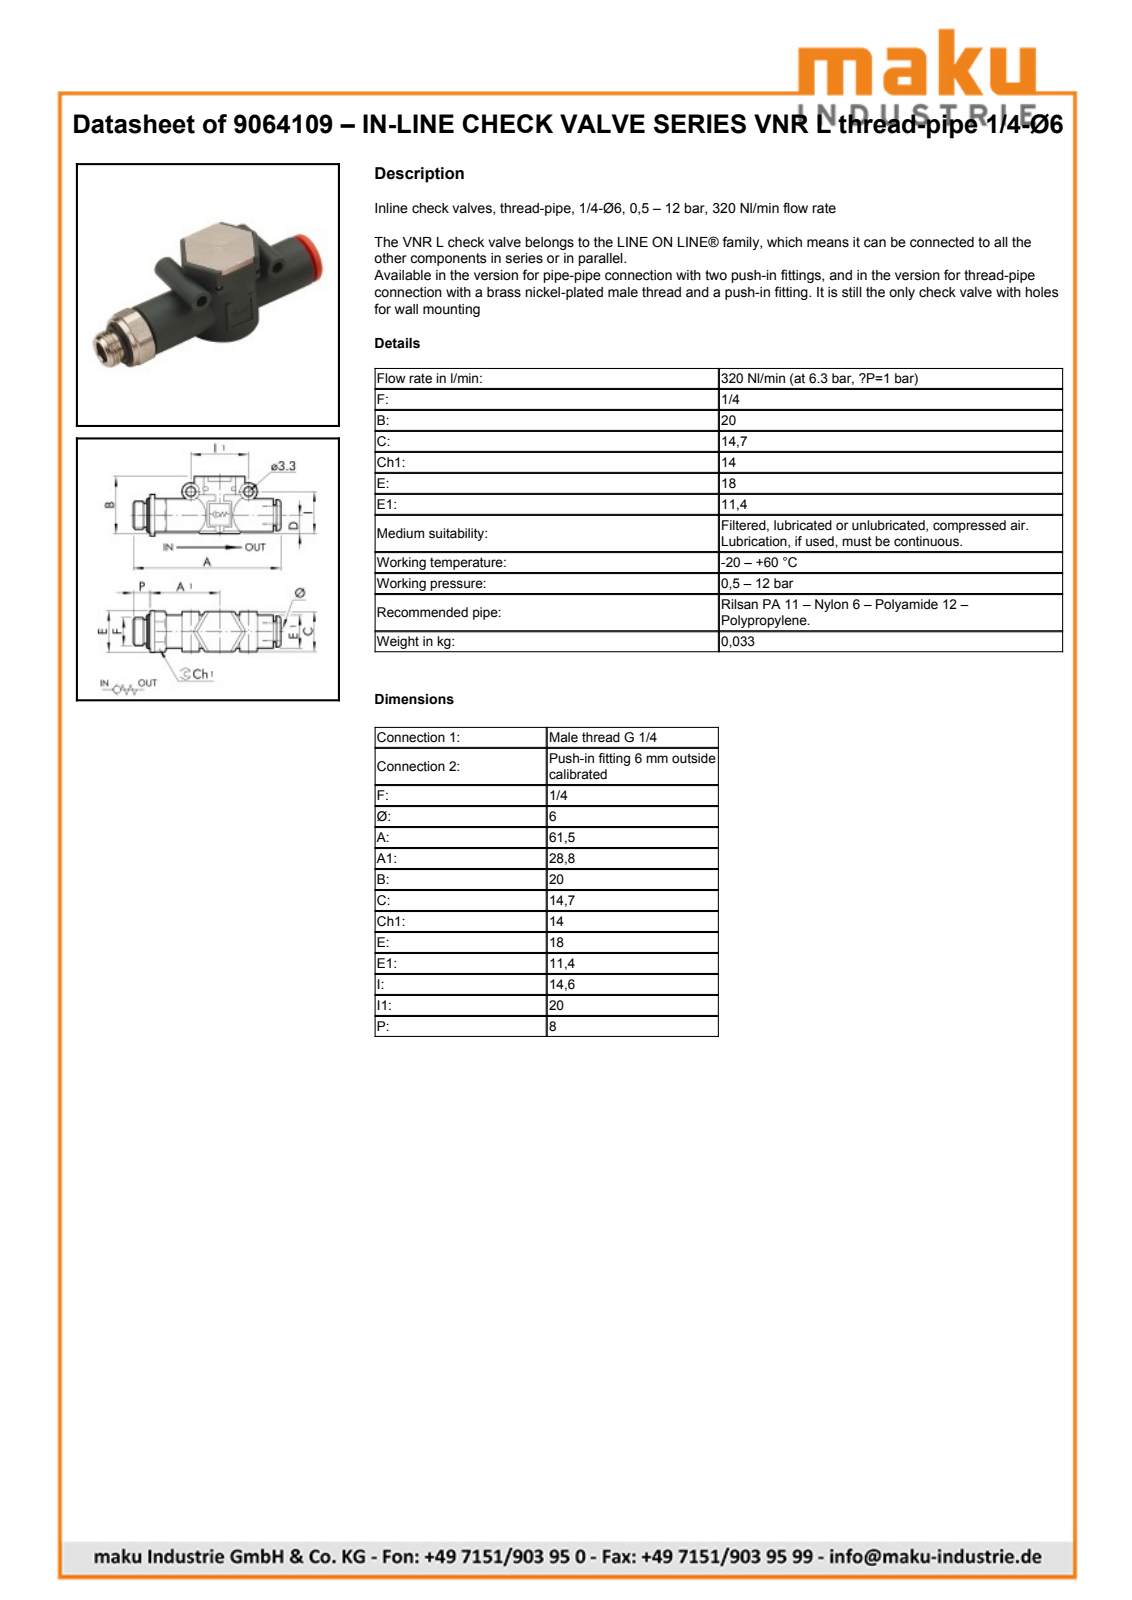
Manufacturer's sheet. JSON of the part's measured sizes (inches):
{"part_name": "9064109; LINE-ON-LINE D6 VSR-L body; LINE-ON-LINE D6 VNR-L bushing; LINE-ON-LINE D6-1/4 thread port (+1 more)", "step_written_by": "PARTsolutions (AUTOMOTIVE_DESIGN)", "units": "inches", "bodies": {"solids": 4, "faces": 146, "planar": 84, "cylindrical": 51, "other": 11}, "overall_size": [2.413, 0.89, 0.709], "volume_in3": 0.385, "surface_area_in2": 11.36, "round_holes": [[0.13, 2], [0.138, 1], [0.157, 1], [0.236, 1], [0.244, 1], [0.291, 1], [0.315, 1], [0.354, 1], [0.378, 1], [0.406, 1], [0.457, 1]], "round_bosses_or_shafts": [[0.236, 2], [0.709, 1], [0.583, 1], [0.518, 1], [0.449, 1], [0.437, 1], [0.433, 1], [0.394, 1]], "partial_cylinders_radius": [[0.313, 2], [0.148, 1], [0.311, 1], [0.36, 1]], "face_to_face_distances": [0.063, 0.079, 0.551, 0.724, 0.787, 0.386, 0.041, 1.613, 0.055, 0.307], "hole_center_spacings": [0.502, 0.787]}
